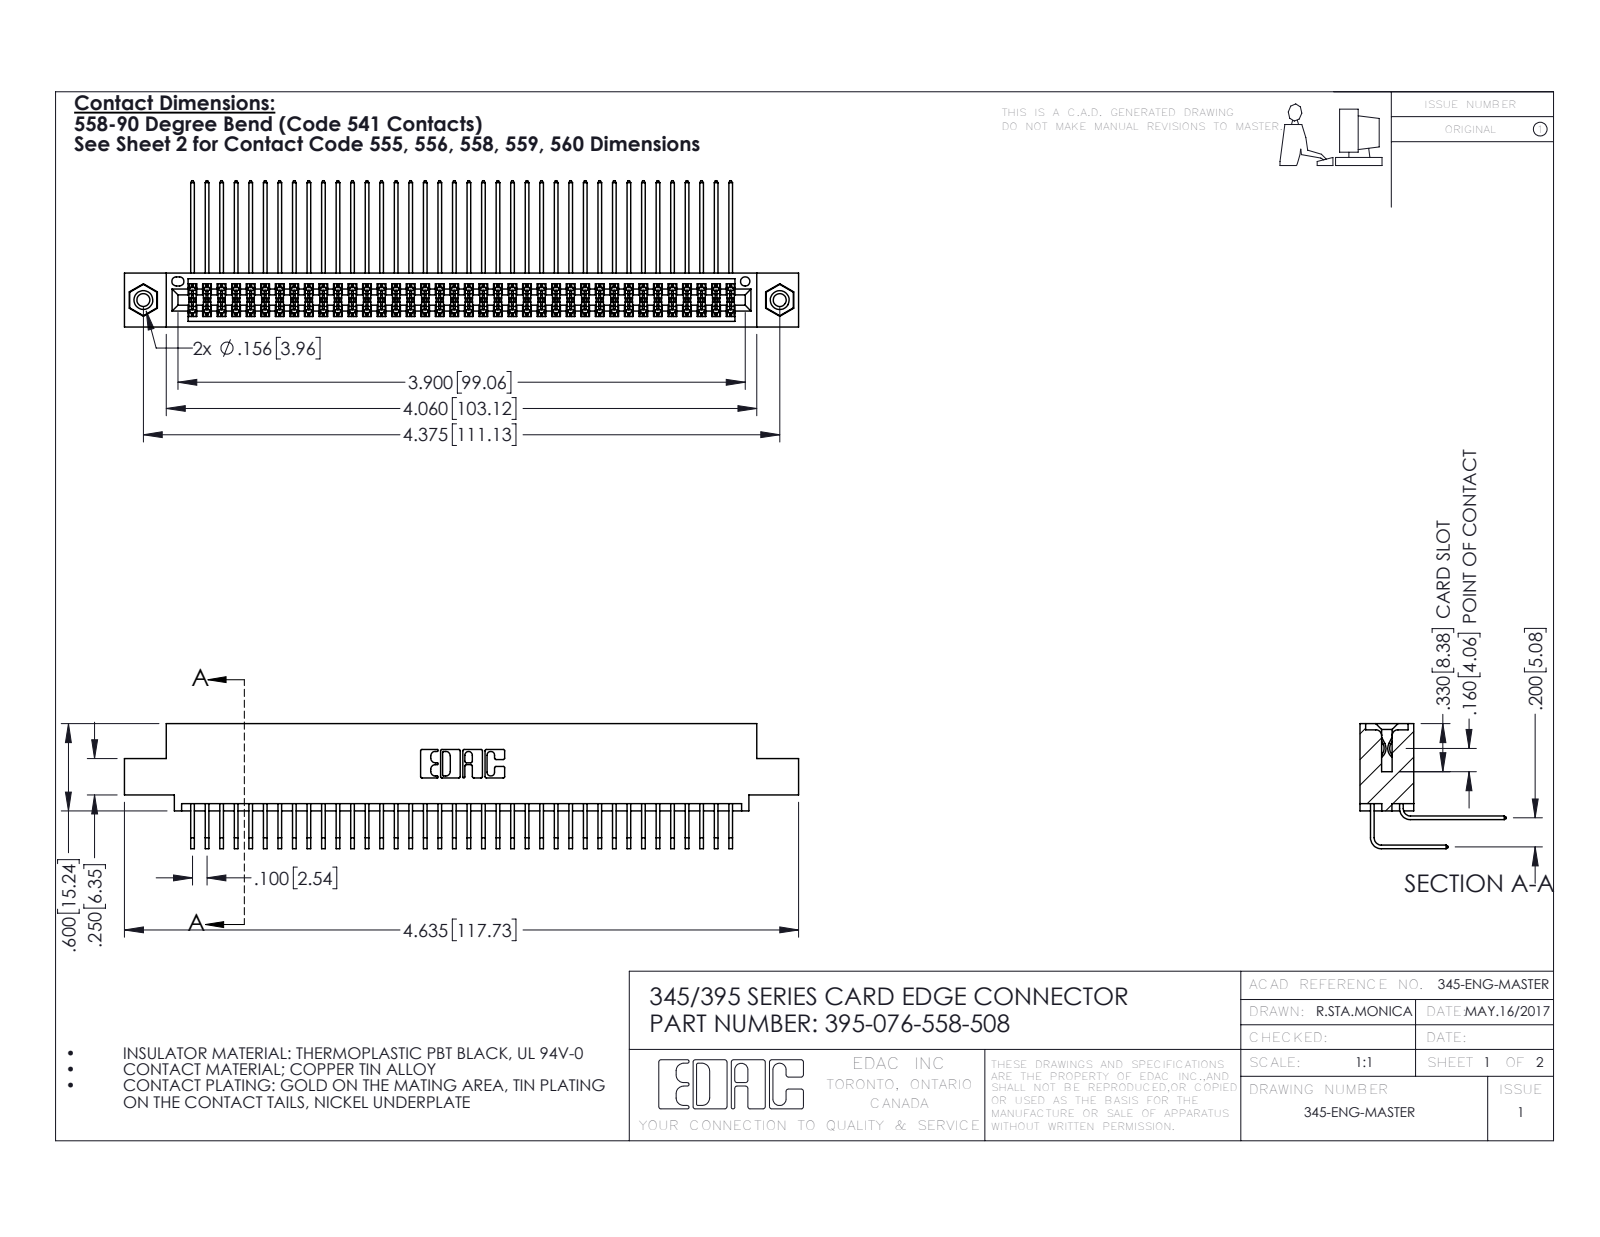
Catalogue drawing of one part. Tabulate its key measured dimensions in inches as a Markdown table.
| quantity | value |
| --- | --- |
| part name | 345-292-001_558 Tail - 2; 345-292-001_558 559 Tail - 1; 345 Part_0.110 Offset - 0.156 Dia-TI; 345-250-001_345-250-003-102 (+1 more) |
| STEP written by | SolidWorks 2016 (CONFIG_CONTROL_DESIGN) |
| units | inches |
| bodies | 79 solids, 4142 faces (2776 planar, 1350 cylindrical, 16 other) |
| overall size | 4.635 × 1.005 × 0.859 |
| volume | 0.718 in³ |
| surface area | 30.18 in² |
| round holes (diameter × count) | 0.089 × 2, 0.125 × 2, 0.156 × 2, 0.064 × 1 |
| round bosses / shafts (diameter × count) | 0.155 × 2 |
| partial cylindrical surfaces (radius × count) | 0.006 × 114, 0.01 × 22, 0.007 × 6, 0.031 × 6, 0.026 × 3, 0.014 × 2, 0.019 × 2, 0.022 × 2 |
| main face-to-face distances | 0.072, 0.298, 0.2, 0.37, 0.098, 0.272, 0.025, 0.225, 0.025, 0.175 |
| hole center spacings | 0.27, 4.139, 4.375 |
